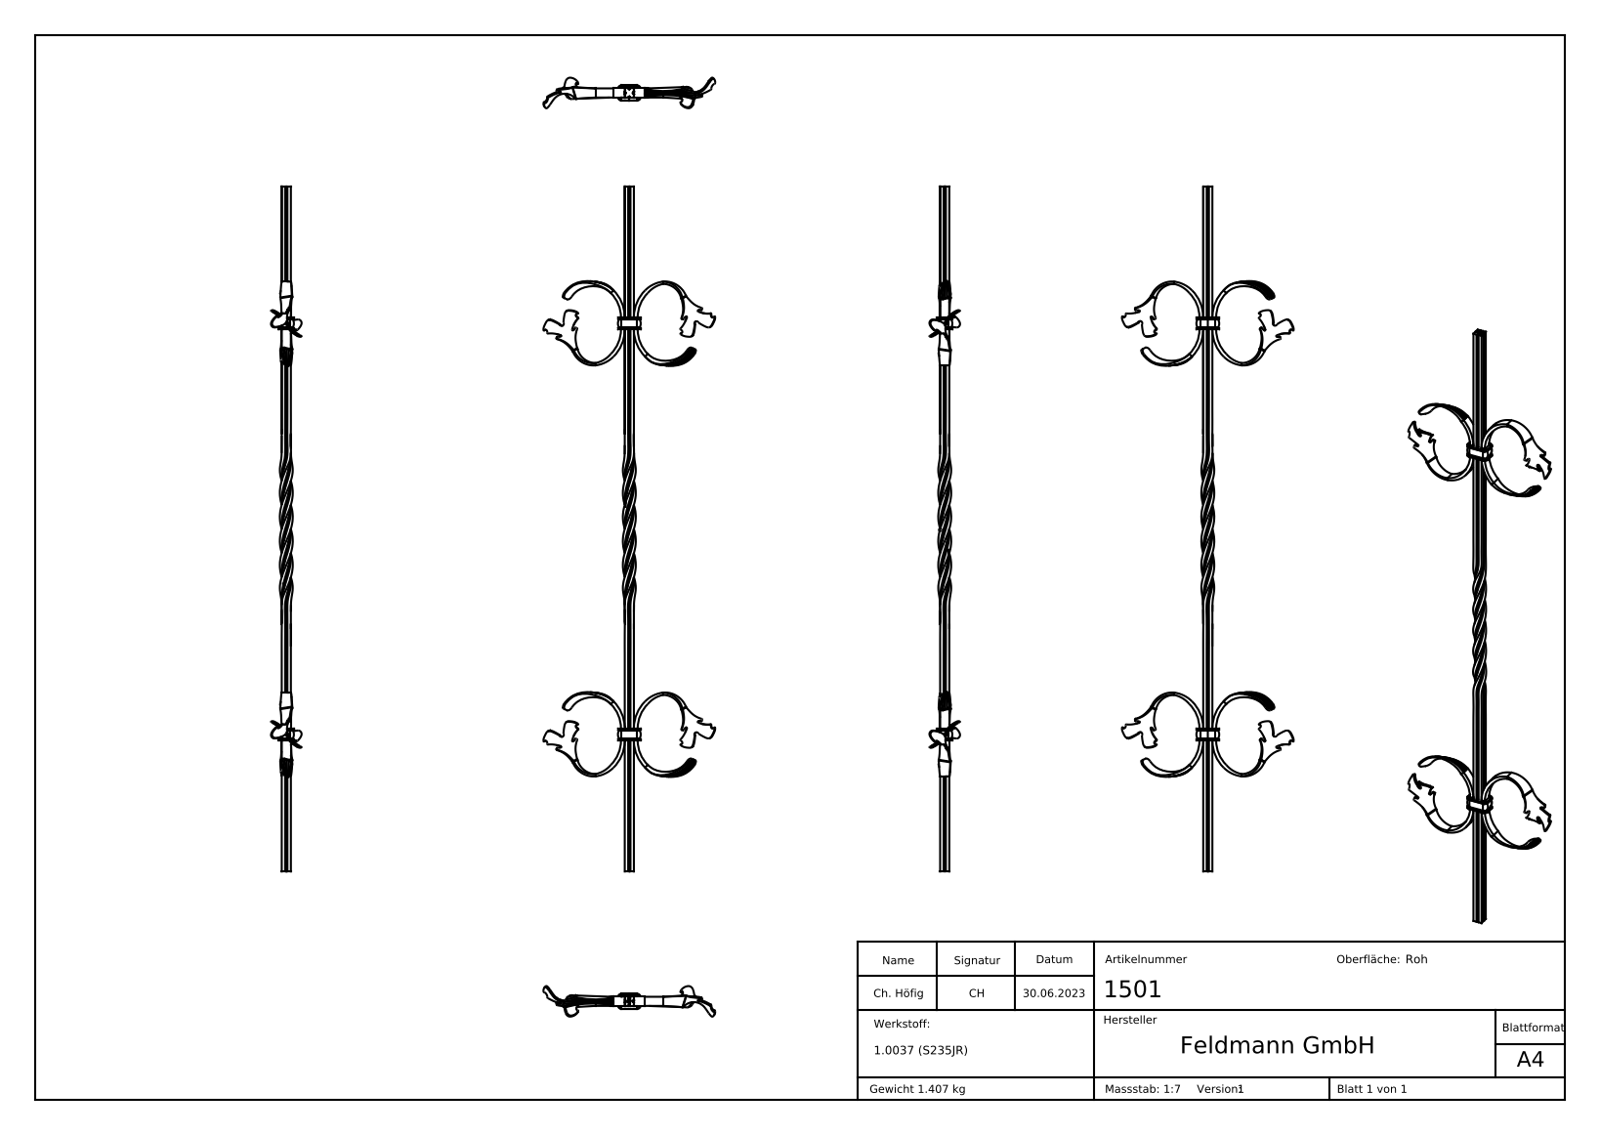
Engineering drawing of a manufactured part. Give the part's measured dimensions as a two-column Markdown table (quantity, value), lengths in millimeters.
| quantity | value |
| --- | --- |
| part name | 1501 |
| STEP written by | SolidWorks 2018 (CONFIG_CONTROL_DESIGN) |
| units | millimeters |
| bodies | 7 solids, 729 faces (269 planar, 110 cylindrical, 350 other) |
| overall size | 900 × 225.64 × 40.18 |
| volume | 178 177 mm³ |
| surface area | 96 835 mm² |
| partial cylindrical surfaces (radius × count) | 0.5 × 48, 45.19 × 8, 50.19 × 8, 10 × 6, 1 × 4, 5 × 4 |
| main face-to-face distances | 12, 4.9, 17.12, 16, 540, 22.01, 4.89, 17.11, 12.22, 22.02 |
